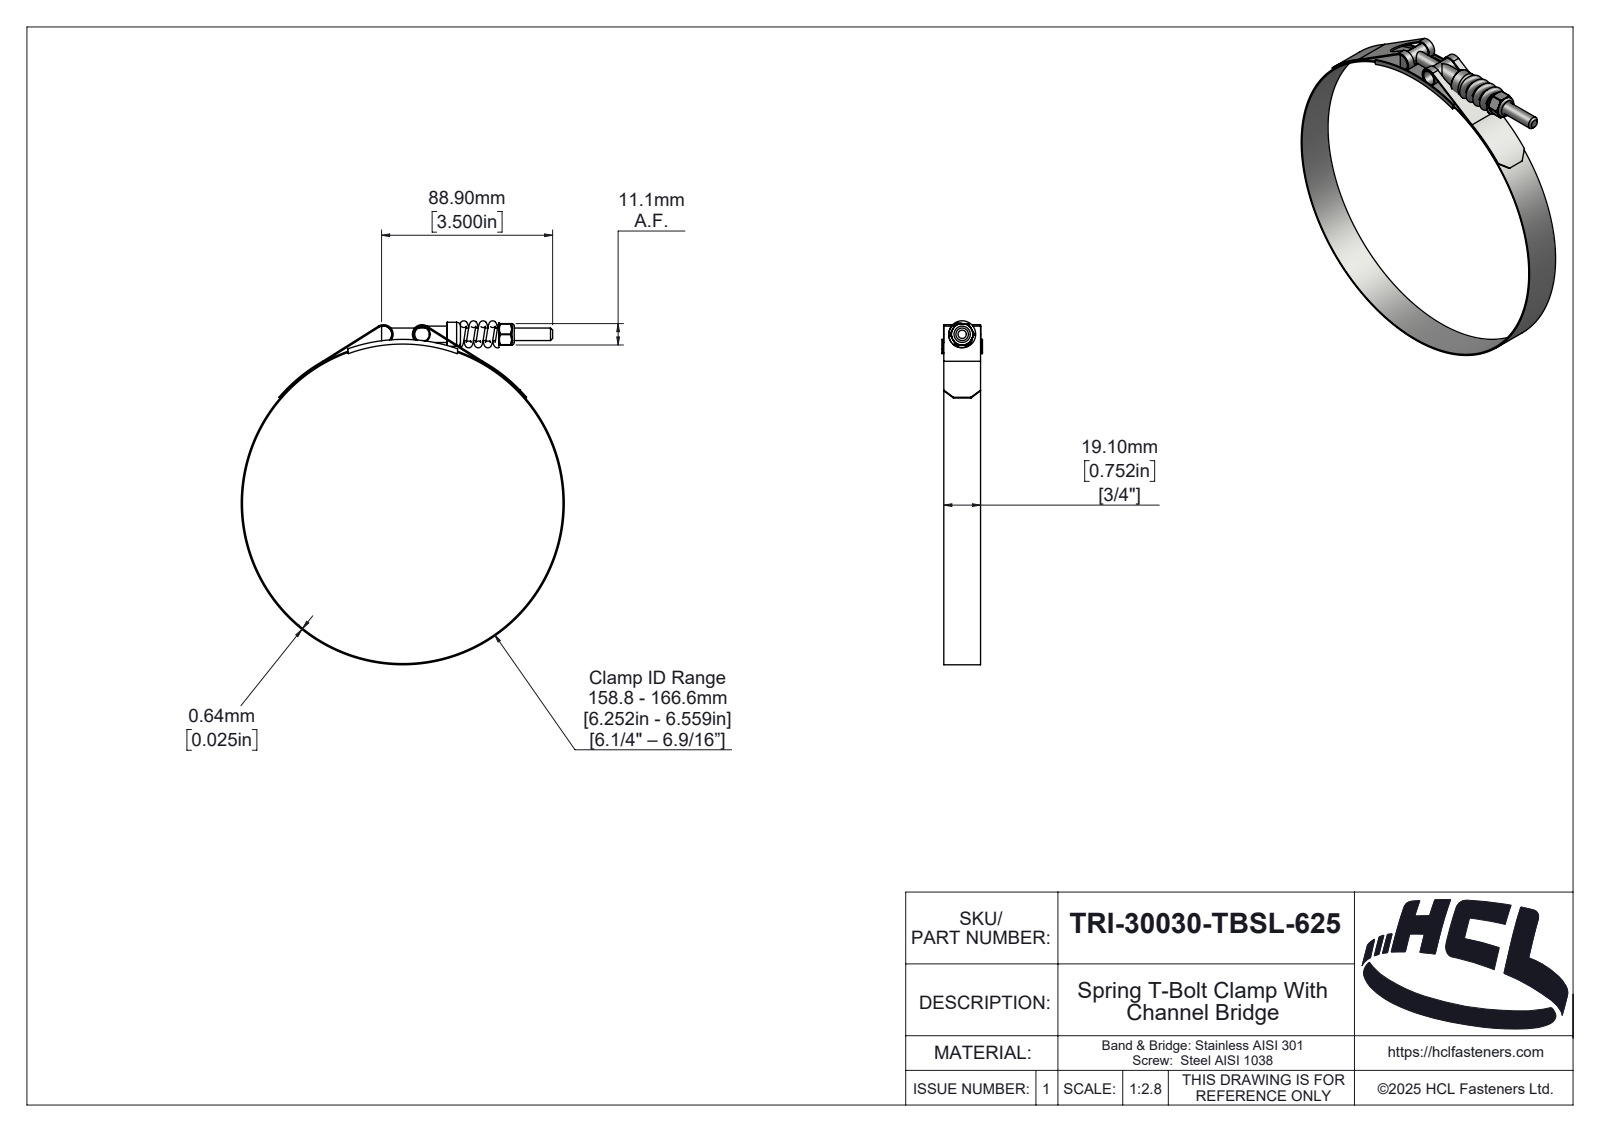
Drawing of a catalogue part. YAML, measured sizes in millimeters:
part_name: "TRI-30030-TBSL-625"
step_written_by: "SolidWorks 2025 (AUTOMOTIVE_DESIGN)"
units: millimeters
bodies: {solids: 7, faces: 332, planar: 48, cylindrical: 122, other: 162}
overall_size: [178.69, 167.88, 21.1]
volume: 15100
surface_area: 34721
round_holes:
  - {diameter: 5.4, count: 1}
  - {diameter: 6.35, count: 1}
  - {diameter: 6.5, count: 1}
  - {diameter: 7.52, count: 1}
  - {diameter: 166.6, count: 1}
round_bosses_or_shafts:
  - {diameter: 8.52, count: 2}
  - {diameter: 167.88, count: 1}
  - {diameter: 12.52, count: 1}
partial_cylinders:
  - {radius: 0.39, count: 6}
  - {radius: 0.5, count: 2}
  - {radius: 4.36, count: 2}
  - {radius: 5, count: 2}
  - {radius: 0.59, count: 1}
  - {radius: 2.42, count: 1}
  - {radius: 3.03, count: 1}
  - {radius: 3.19, count: 1}
face_to_face_distances: [0.64, 19.1, 1, 20.1, 20.46, 0.36, 19.46, 21.1, 61, 11.11]
hole_center_spacings: [88.3]
